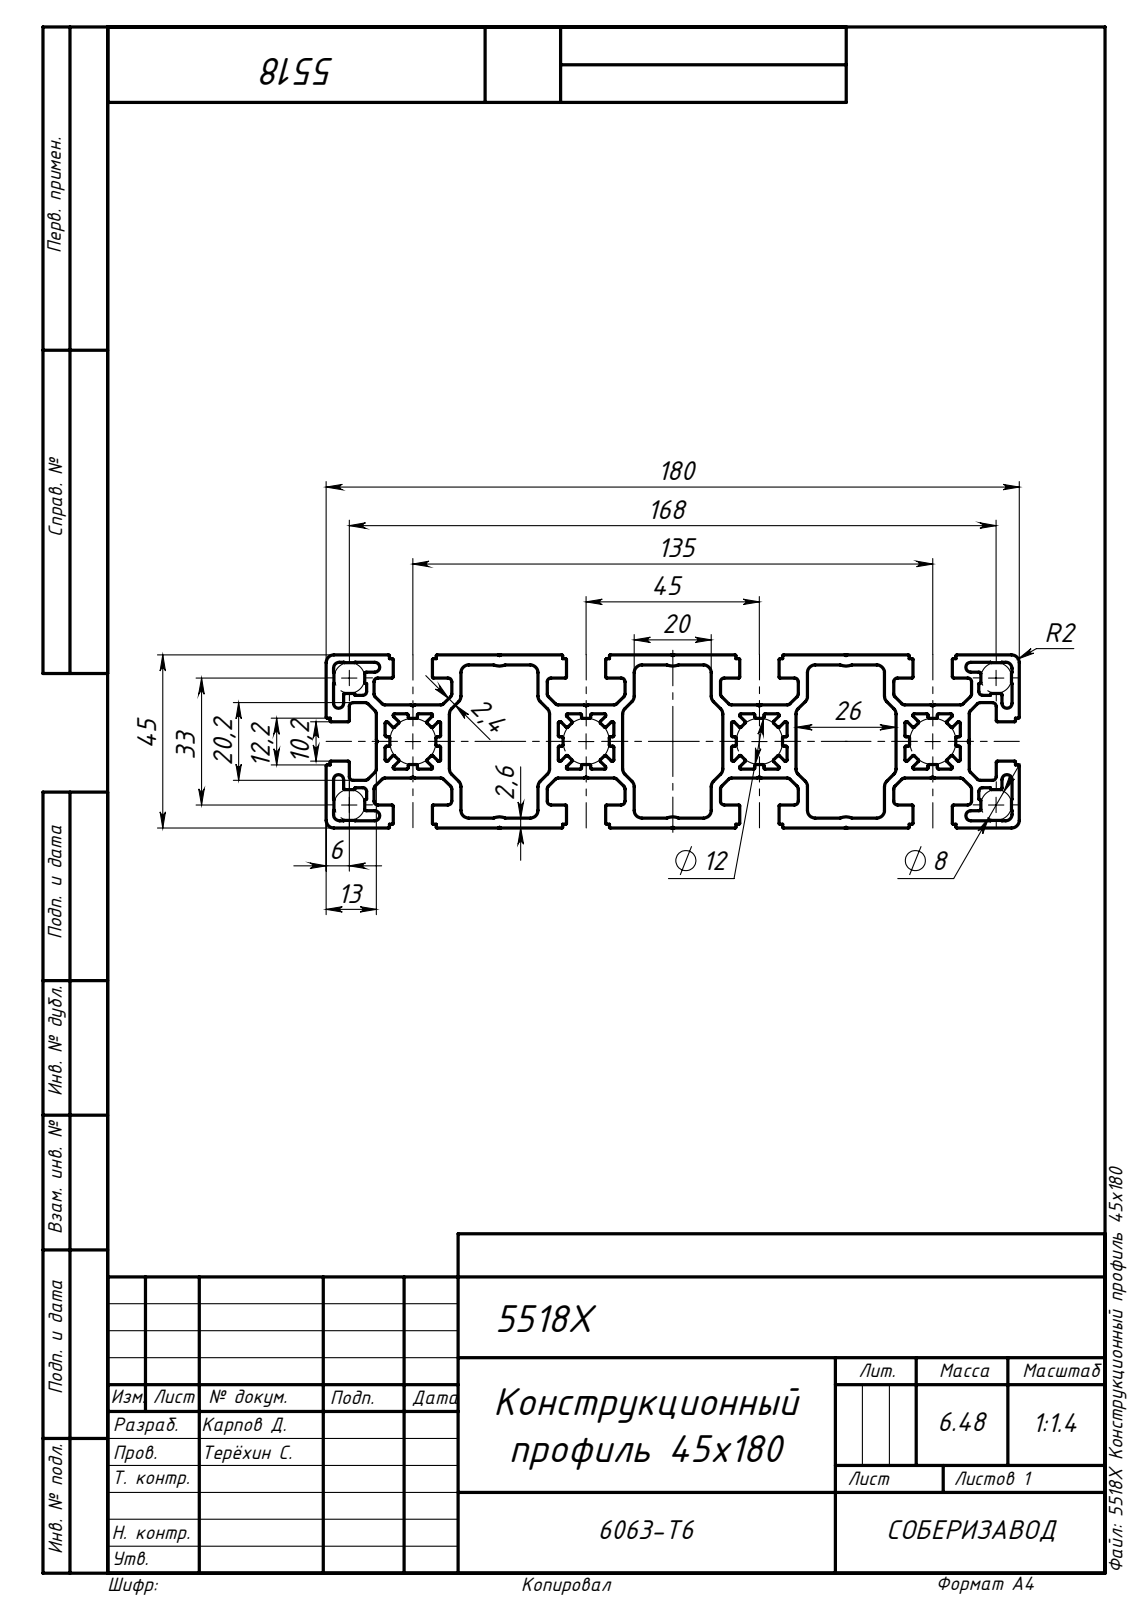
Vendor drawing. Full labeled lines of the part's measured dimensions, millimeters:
Part name (STEP PRODUCT): 5518X Конструкционный профиль 45х180
STEP written by: SolidWorks 2019 (AUTOMOTIVE_DESIGN)
Units: millimetres
Bodies: 1 solid, 902 faces (476 planar, 426 cylindrical, 0 other)
Overall size (bounding box): 1000 × 180 × 45
Volume: 2 401 000 mm³ · Surface area: 1 725 000 mm²
Partial cylindrical surfaces — rounded edges, fillets, slot ends (radius × count): R0.25 ×132, R0.3 ×120, R1 ×64, R2 ×40, R0.4 ×24, R0.35 ×8, R1.3 ×8, R4 ×6
Main face-to-face distances: 45, 32, 13, 19, 26, 2.6, 90, 42.4, 10.4, 29.4
